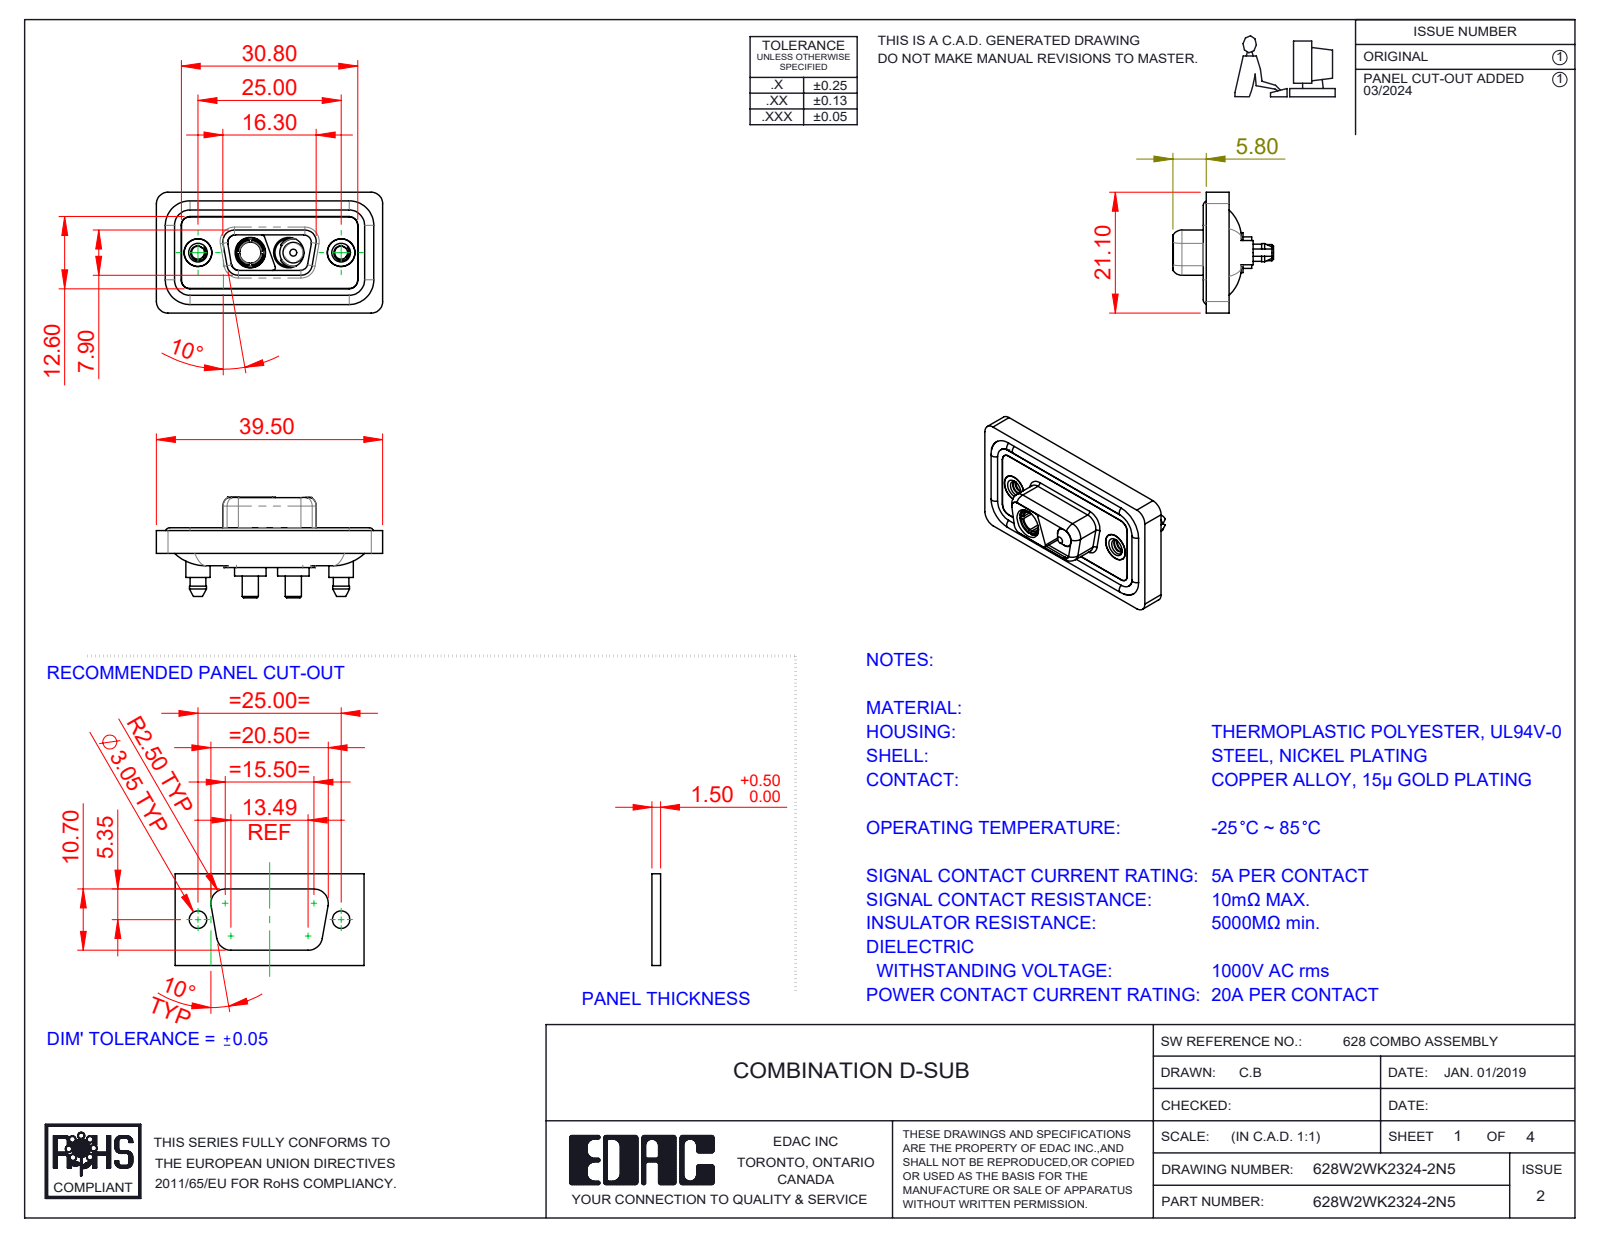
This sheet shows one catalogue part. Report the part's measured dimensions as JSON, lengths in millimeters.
{"part_name": "628Combo Threaded Boardlock_5; 628Combo Waterproof Housing_09 Contacts; 628W2WK2324-2N5; Power Socket_20A S (+4 more)", "step_written_by": "SolidWorks 2023 (CONFIG_CONTROL_DESIGN)", "units": "millimeters", "bodies": {"solids": 11, "faces": 550, "planar": 160, "cylindrical": 263, "other": 127}, "overall_size": [39.5, 21.1, 17.55], "volume_mm3": 4737, "surface_area_mm2": 7677, "round_holes": [[4.85, 4], [2.26, 2], [4, 2], [4.05, 2], [5, 2], [5.3, 2], [3.7, 1]], "round_bosses_or_shafts": [[1.6, 4], [5.5, 2], [5.4, 2], [5.2, 2], [4.95, 2], [4.8, 2], [4.75, 2], [4.25, 2]], "partial_cylinders_radius": [[1.5, 24], [2, 18], [1.6, 10], [1.35, 8], [0.5, 6], [0.25, 4], [0.6, 4], [0.65, 4]], "face_to_face_distances": [0.4, 1.1, 2.9, 1.6, 0.5, 1.8, 5.65, 1.5, 4, 5.35], "hole_center_spacings": [9.14, 15.86, 6.72, 25]}
